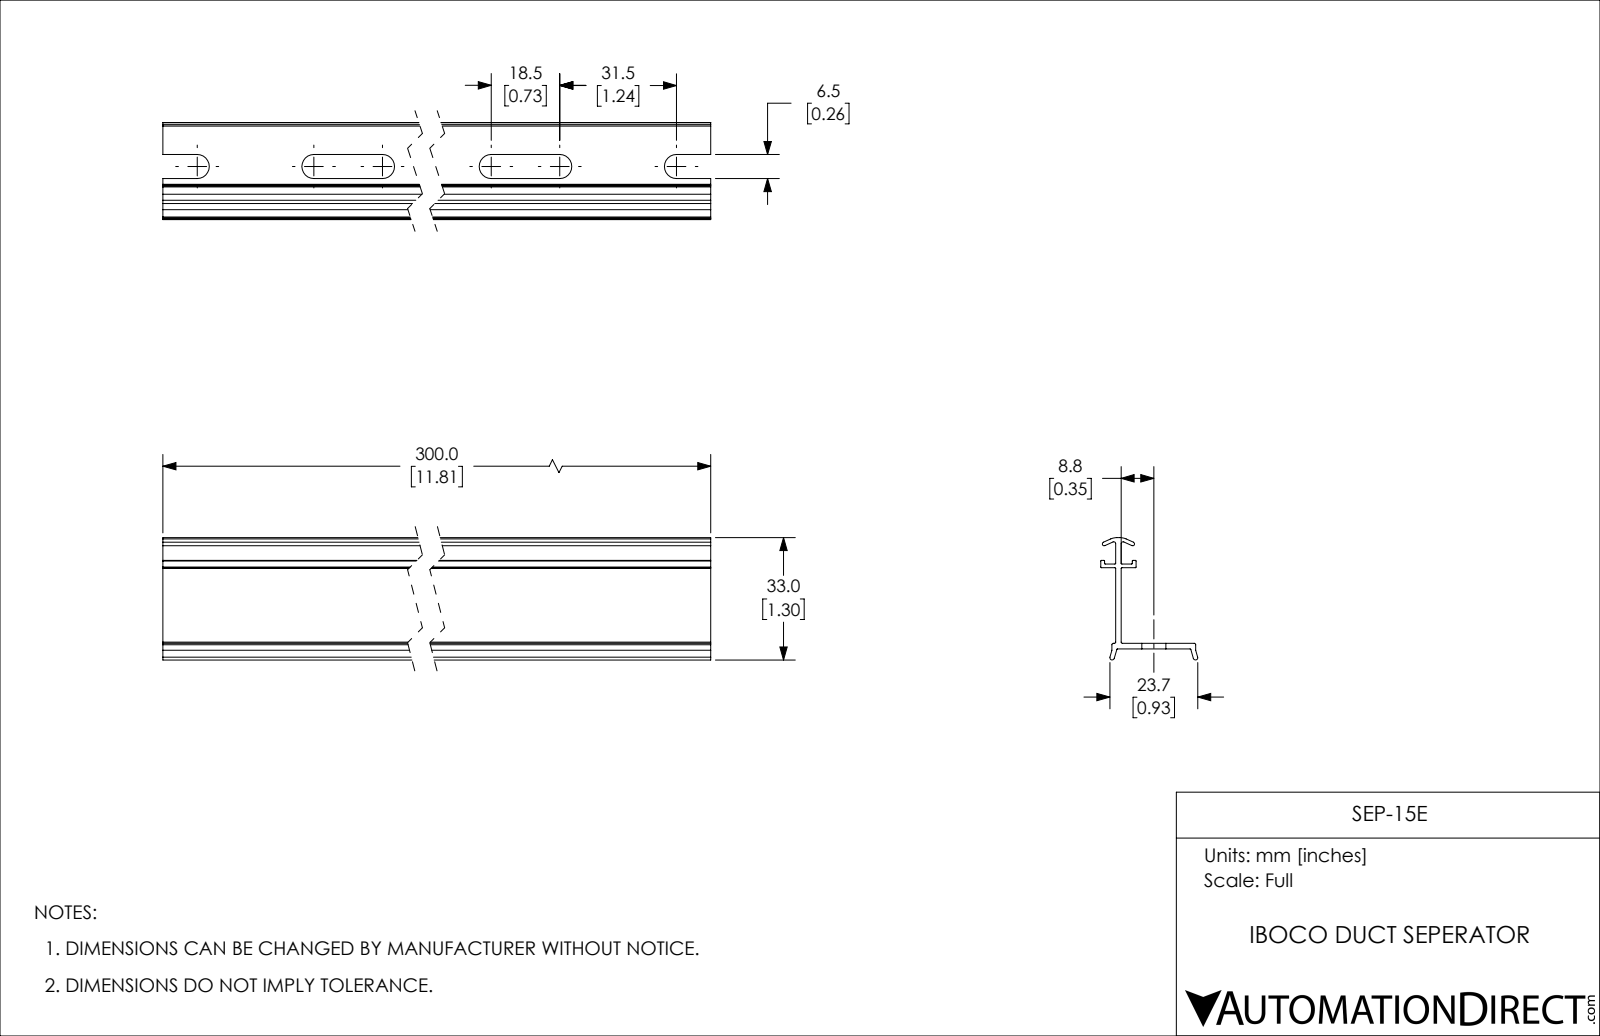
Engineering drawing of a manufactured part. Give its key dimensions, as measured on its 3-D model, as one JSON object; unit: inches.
{"part_name": "SEP-15E", "step_written_by": "SolidWorks 2019 (CONFIG_CONTROL_DESIGN)", "units": "inches", "bodies": {"solids": 1, "faces": 91, "planar": 46, "cylindrical": 45, "other": 0}, "overall_size": [11.811, 1.299, 1.03], "volume_in3": 1.772, "surface_area_in2": 67.19, "partial_cylinders_radius": [[0.008, 14], [0.128, 12], [0.02, 4], [0.012, 2], [0.016, 2], [0.024, 2], [0.157, 2]], "face_to_face_distances": [0.059, 0.039, 0.861, 0.802, 0.901, 0.842, 0.047, 0.217, 0.157, 0.118]}
